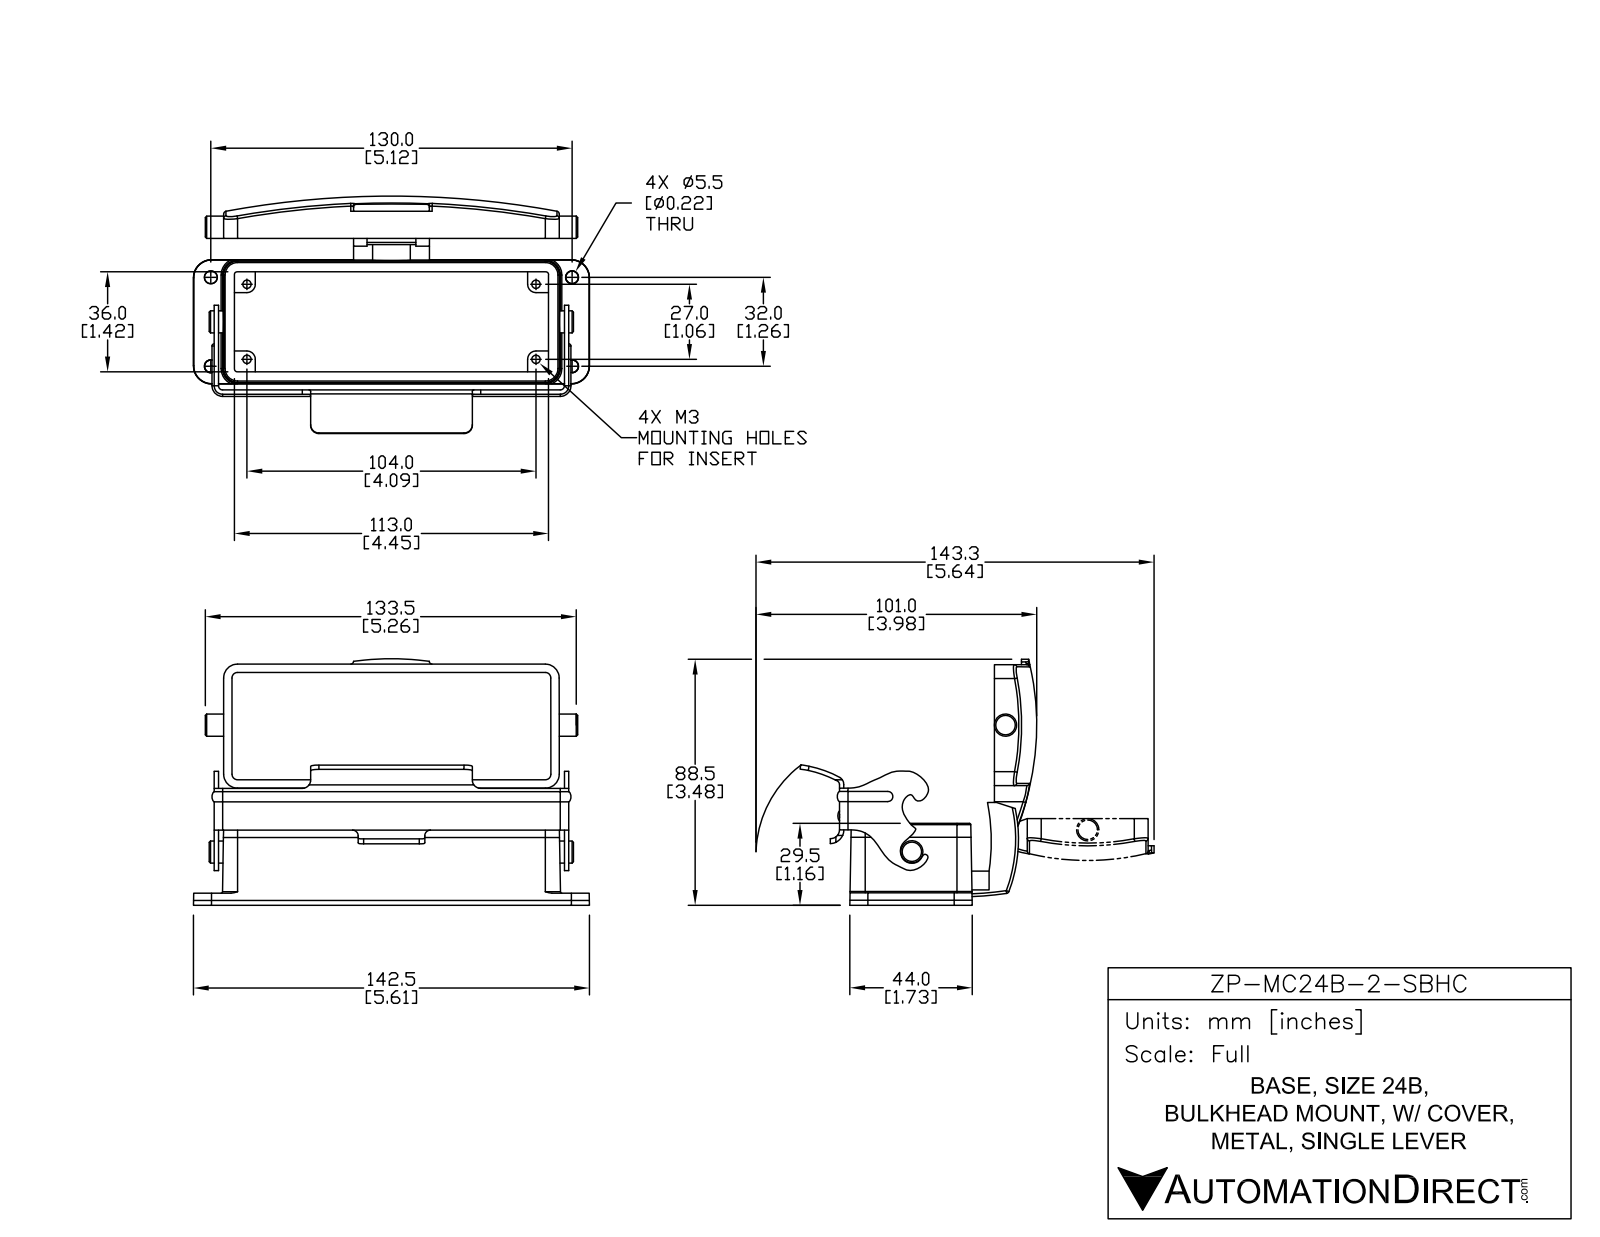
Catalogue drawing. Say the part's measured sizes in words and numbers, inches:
The part is named "ZP-MC24B-2-SBHC". Its 3-D file was written by "SolidWorks 2017 (AUTOMOTIVE_DESIGN)". It is 3 solids with 309 faces: 127 planar, 84 cylindrical and 98 other. Overall it measures 5.61 by 3.449 by 3.363 inches. Its volume is 5.068 cubic inches and its surface area 84.3 square inches. Round holes: 4 of diameter 0.118, 1 of diameter 0.079. Round bosses or shafts: 1 of diameter 0.315, 1 of diameter 0.313, 1 of diameter 0.268. Partial cylindrical surfaces (rounded edges, fillets, slot ends): 8 of radius 0.079, 8 of radius 0.118, 6 of radius 0.02, 6 of radius 0.197, 4 of radius 0.041, 3 of radius 0.039, 2 of radius 0.059, 2 of radius 0.12. The main face-to-face distances are 0.118, 1.594, 1.417, 0.061, 1.587, 1.673, 0.256, 1.89, 2.146, 0.472. The hole center spacings are 1.063, 4.094, 4.23.
